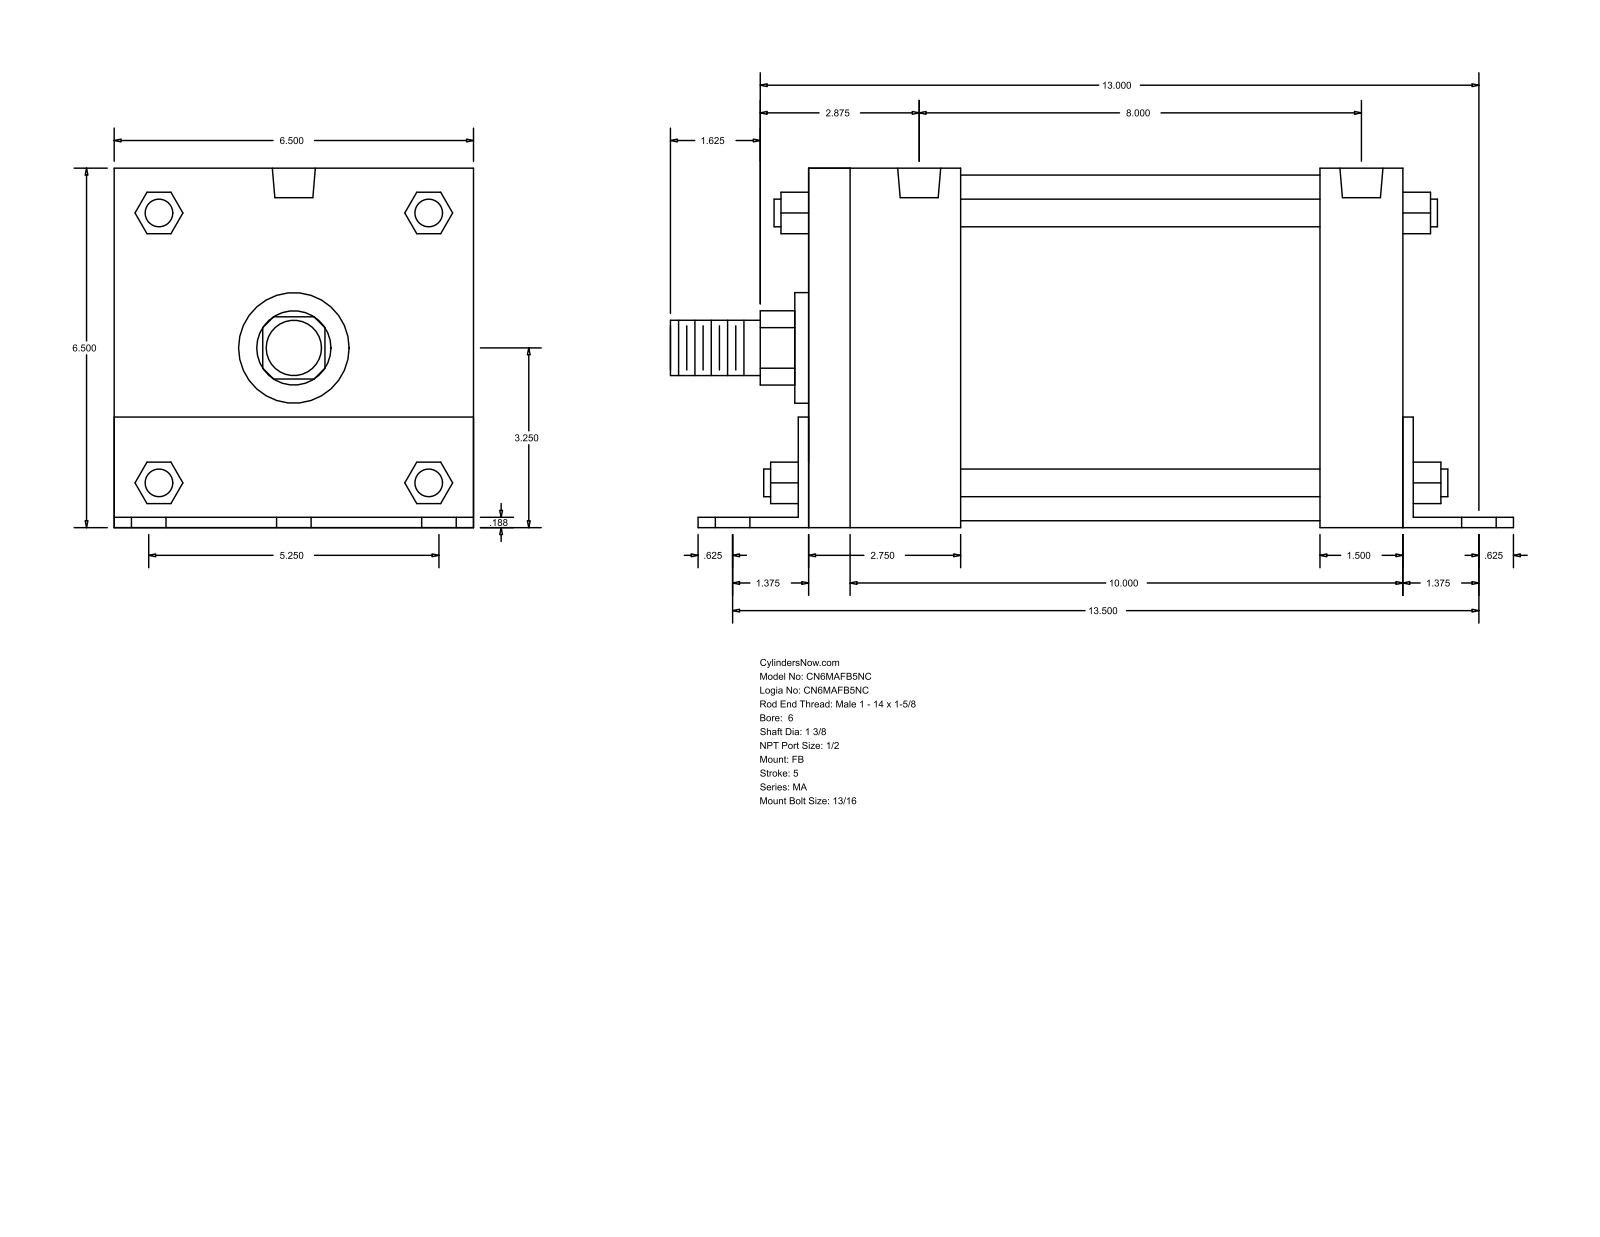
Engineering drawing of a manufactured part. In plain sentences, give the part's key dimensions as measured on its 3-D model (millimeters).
The part is named "MA_FB__0600_1.375". Its 3-D file was written by "GSSL Pune (CONFIG_CONTROL_DESIGN)". It is 0 solids with 140 faces: 105 planar, 35 cylindrical and 0 other. Overall it measures 384.18 by 165.15 by 165.1 millimeters. Round holes: 6 of diameter 20.64, 4 of diameter 17.46, 2 of diameter 19.77. Round bosses or shafts: 4 of diameter 12.7, 1 of diameter 158.75, 1 of diameter 50.8, 1 of diameter 34.92, 1 of diameter 25.4. Partial cylindrical surfaces (rounded edges, fillets, slot ends): 1 of radius 17.06, 1 of radius 32.05. The main face-to-face distances are 165.1, 4.76, 269.87, 165.15, 4.71, 160.39, 4.77, 38.1, 42.86, 279.4. The hole center spacings are 66.67, 346.2, 339.72, 83.81, 85.78, 108.6, 133.34, 200.02.
